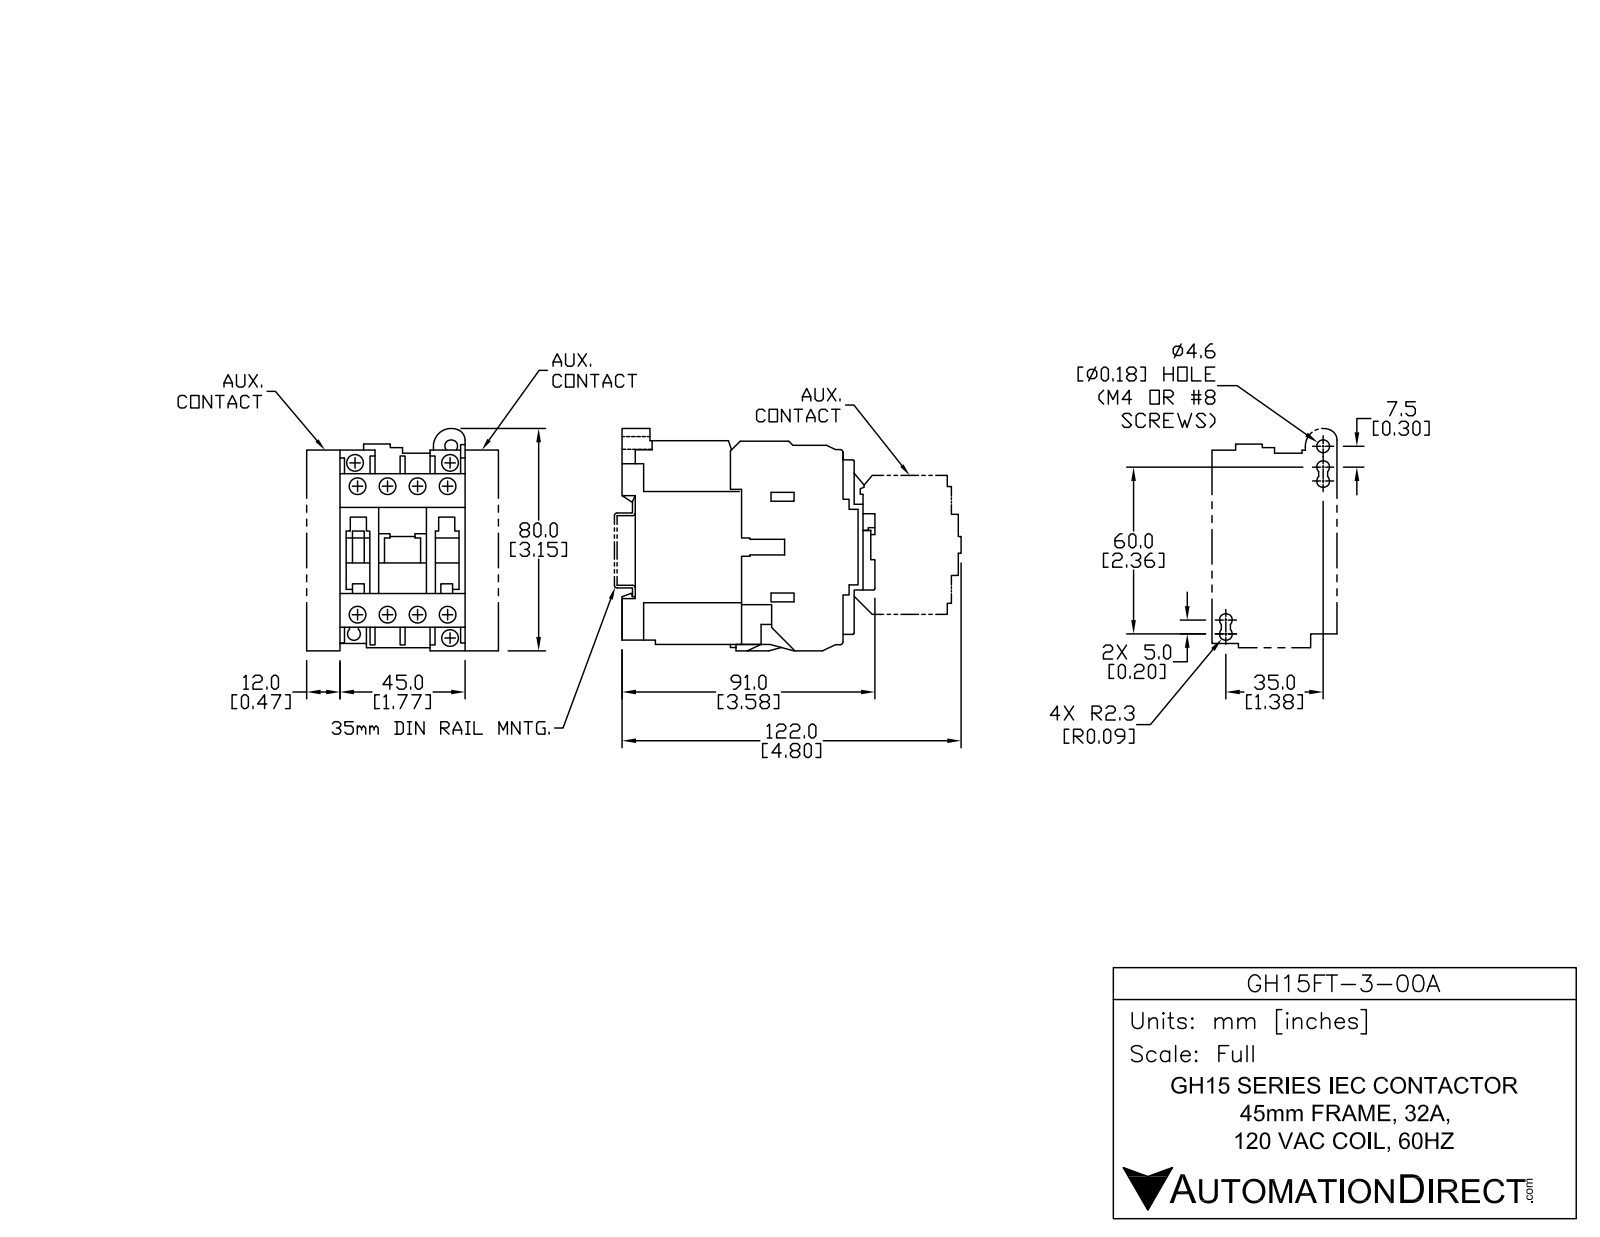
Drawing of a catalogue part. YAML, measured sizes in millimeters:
part_name: "GH15FT-3-00A"
step_written_by: "SolidWorks 2009 (AUTOMOTIVE_DESIGN)"
units: millimeters
bodies: {solids: 1, faces: 676, planar: 479, cylindrical: 51, other: 146}
overall_size: [91.5, 80, 45]
volume: 218392
surface_area: 38409
round_holes:
  - {diameter: 7, count: 6}
  - {diameter: 6.25, count: 3}
  - {diameter: 4.6, count: 1}
partial_cylinders:
  - {radius: 1, count: 9}
  - {radius: 2.3, count: 8}
  - {radius: 3, count: 2}
  - {radius: 4.99, count: 1}
  - {radius: 5, count: 1}
face_to_face_distances: [45, 15, 7.75, 35.5, 14, 1, 9.5, 43.25, 54, 1.75]
hole_center_spacings: [14.5, 55.91, 54, 29, 61.29, 4.67, 5.04, 5.89]
